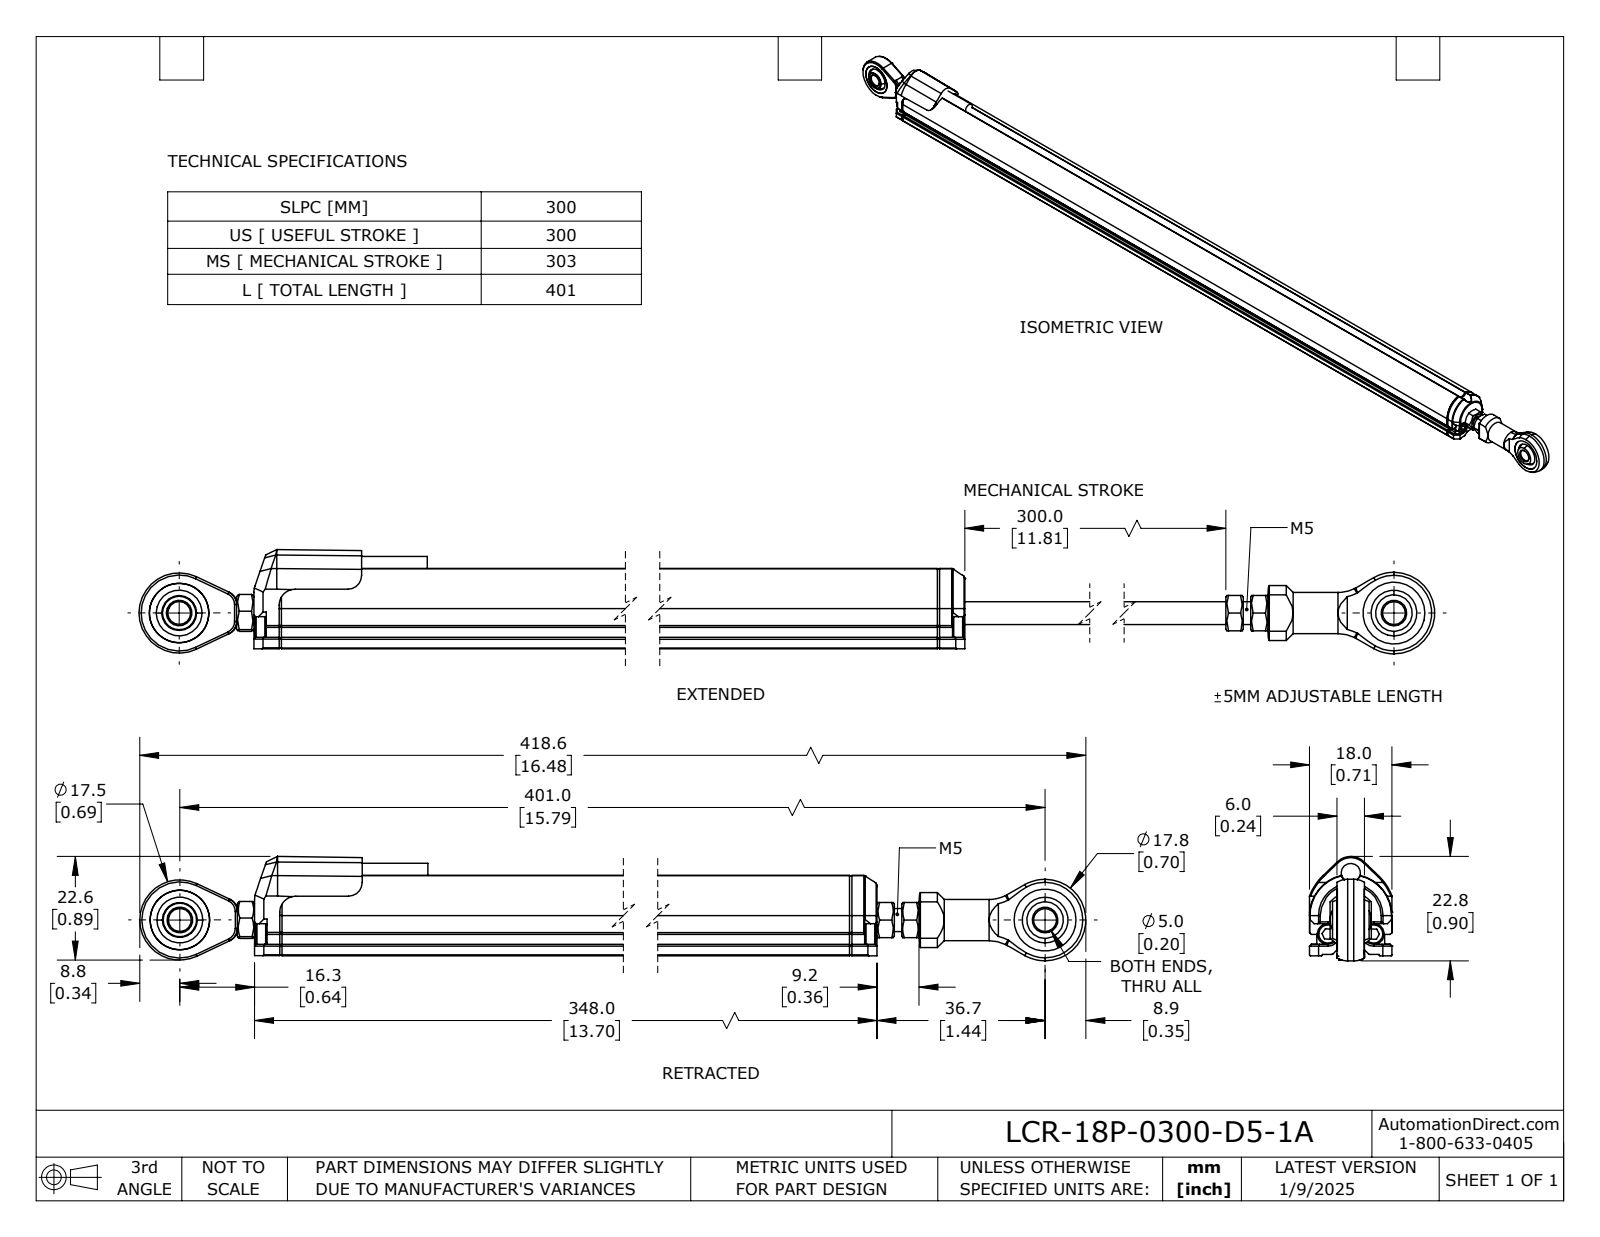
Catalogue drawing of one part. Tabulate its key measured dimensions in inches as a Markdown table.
| quantity | value |
| --- | --- |
| part name | LCR-18P-0300-D5-1A |
| STEP written by | SolidWorks 2023 (AUTOMOTIVE_DESIGN) |
| units | inches |
| bodies | 20 solids, 515 faces (289 planar, 136 cylindrical, 90 other) |
| overall size | 16.482 × 0.896 × 0.709 |
| volume | 5.931 in³ |
| surface area | 56.42 in² |
| round holes (diameter × count) | 0.197 × 4, 0.102 × 2, 0.104 × 2, 0.394 × 2, 0.213 × 1, 0.272 × 1, 0.512 × 1, 0.531 × 1 |
| round bosses / shafts (diameter × count) | 0.181 × 4, 0.113 × 3, 0.059 × 2, 0.354 × 1, 0.165 × 1, 0.113 × 1 |
| partial cylindrical surfaces (radius × count) | 0.008 × 12, 0.004 × 10, 0.02 × 8, 0.012 × 6, 0.018 × 6, 0.016 × 4, 0.039 × 4, 0.043 × 4 |
| main face-to-face distances | 0.709, 0.063, 0.646, 0.059, 0.071, 0.02, 0.087, 13.248, 0.236, 0.098 |
| hole center spacings | 0.231, 0.394, 0.23, 0.231, 15.787 |
